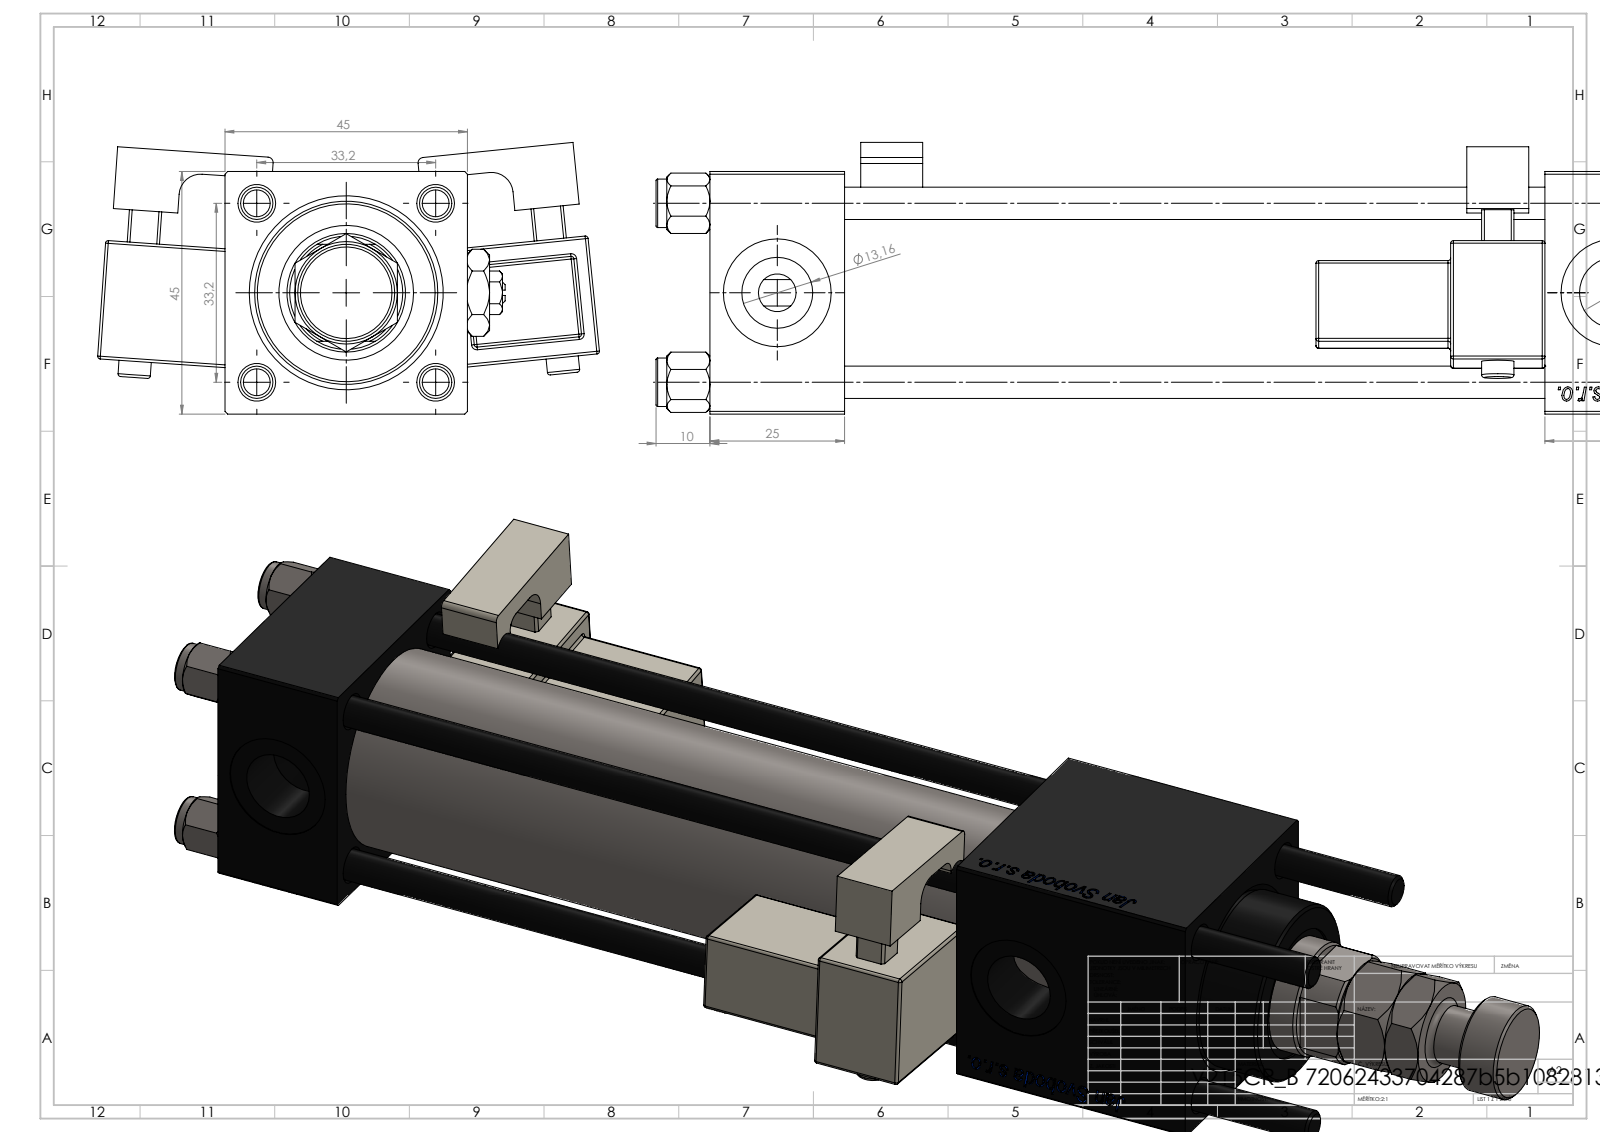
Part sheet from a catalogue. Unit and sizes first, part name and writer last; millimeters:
Units: millimetres
Overall size (bounding box): 271 × 93.14 × 50.4
Round holes (diameter × count): ⌀6 ×4, ⌀7 ×2, ⌀13.16 ×2, ⌀20 ×2, ⌀10.5 ×1, ⌀22 ×1, ⌀24 ×1, ⌀25 ×1, ⌀32 ×1, ⌀33 ×1
Round bosses / shafts (diameter × count): ⌀9 ×4, ⌀6 ×2, ⌀38 ×1, ⌀34 ×1, ⌀18 ×1, ⌀11 ×1
Partial cylindrical surfaces — rounded edges, fillets, slot ends (radius × count): R0.5 ×48, R1 ×2, R2.5 ×2, R4 ×2, R10.5 ×1
Main face-to-face distances: 45, 25, 155, 130, 203, 3, 112.5, 17.5, 44.8, 39.5
Hole centre spacings: 23.48, 33.2, 46.95, 155.5
Volume: 327 354 mm³ · Surface area: 122 481 mm²
Bodies: 16 solids, 1466 faces (556 planar, 152 cylindrical, 758 other)
Part name (STEP PRODUCT): V215CR_B_TYCINKA; V215_VC_A; Zatka_pro_OIL_PORT; V215CR_MSU (+4 more)
STEP written by: SolidWorks 2019 (CONFIG_CONTROL_DESIGN)
